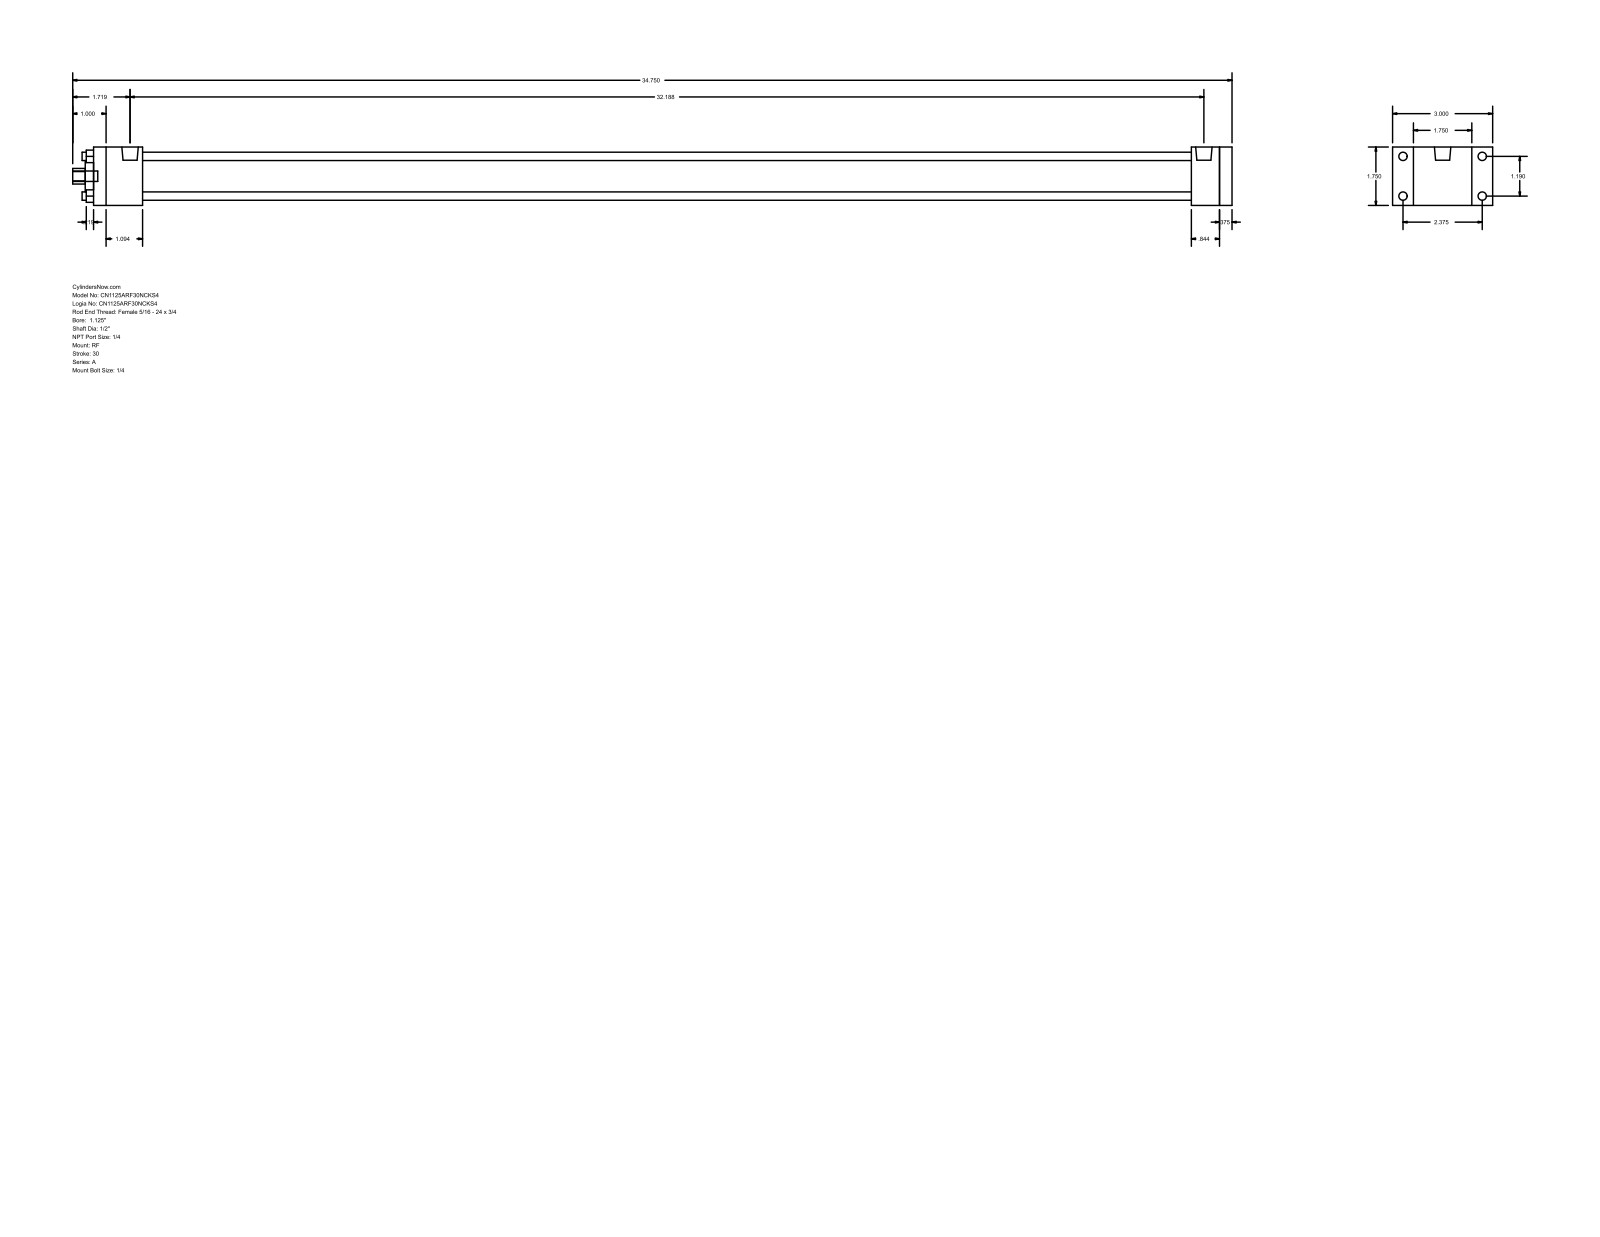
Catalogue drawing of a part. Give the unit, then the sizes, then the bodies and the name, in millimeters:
Units: millimetres
Overall size (bounding box): 882.65 × 76.2 × 44.45
Round holes (diameter × count): ⌀6.35 ×4, ⌀12.7 ×1, ⌀23.81 ×1, ⌀31.88 ×1
Round bosses / shafts (diameter × count): ⌀6.35 ×4, ⌀5.56 ×4, ⌀12.49 ×2, ⌀7.94 ×1
Partial cylindrical surfaces — rounded edges, fillets, slot ends (radius × count): R5.94 ×1
Main face-to-face distances: 44.46, 9.53, 866.77, 857.24, 37.3, 835.81, 798.51, 819.94, 829.47, 21.43
Hole centre spacings: 21.37, 30.22, 42.74
Bodies: 0 solids, 92 faces (64 planar, 28 cylindrical, 0 other)
Part name (STEP PRODUCT): A_RF__0112_0.5
STEP written by: GSSL Pune (CONFIG_CONTROL_DESIGN)
